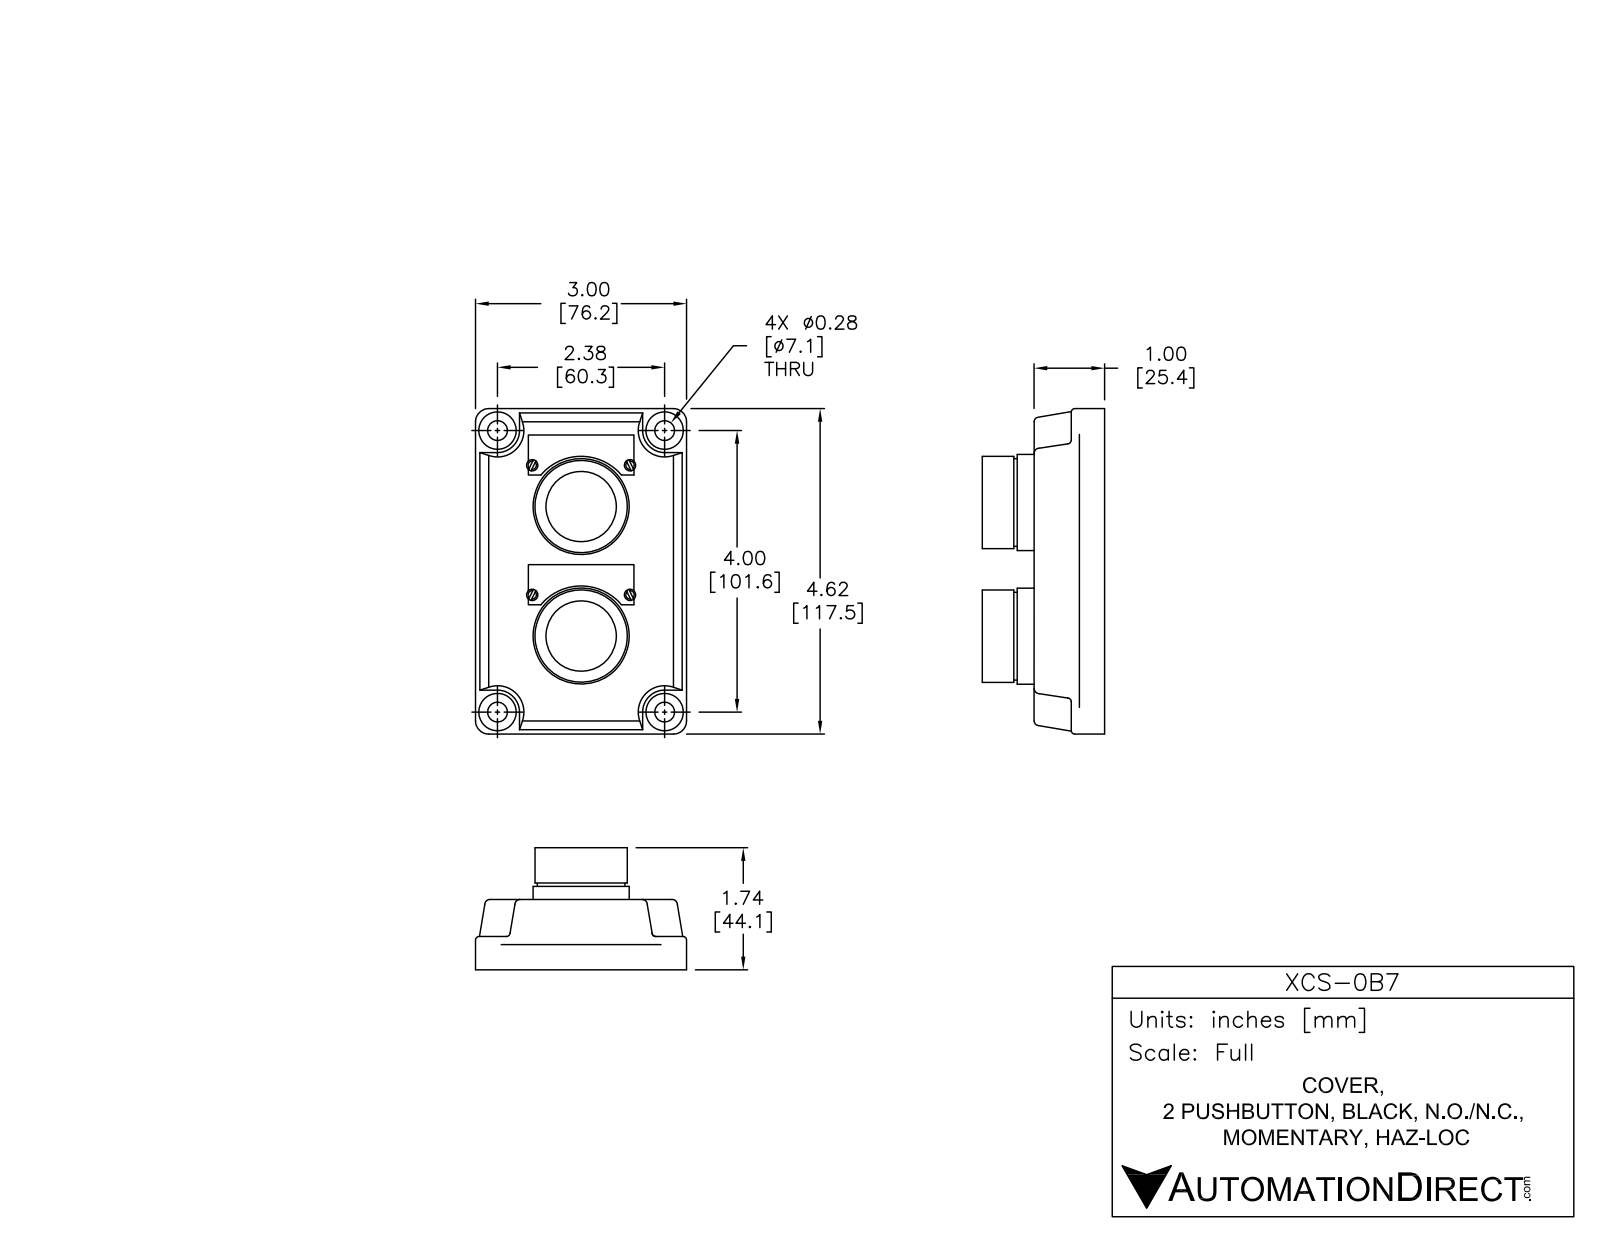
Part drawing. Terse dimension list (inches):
name: XCS-0B7
written by: SolidWorks 2015 (AUTOMOTIVE_DESIGN)
unit: in
bodies: 13 solids, 559 faces (222 planar, 199 cylindrical, 138 other)
size: 4.63 × 3.193 × 3.1
volume: 15.01 in³; area: 107.5 in²
holes: 8× ⌀0.262, 4× ⌀0.27, 2× ⌀1.122
bosses: 6× ⌀0.13, 4× ⌀0.457, 4× ⌀0.25, 2× ⌀1.378, 2× ⌀1.262, 2× ⌀1.033
rounds: 28× R0.01, 16× R0.05, 8× R0.02, 8× R0.055, 8× R0.118, 4× R0.094, 4× R0.1, 4× R0.38
face distances: 0.525, 1.47, 0.945, 0.445, 0.5, 1.025, 0.689, 1.214, 0.256, 0.189
hole spacings: 0.402, 0.8, 0.691, 0.803, 1.06, 1.597, 3.167, 0.622
